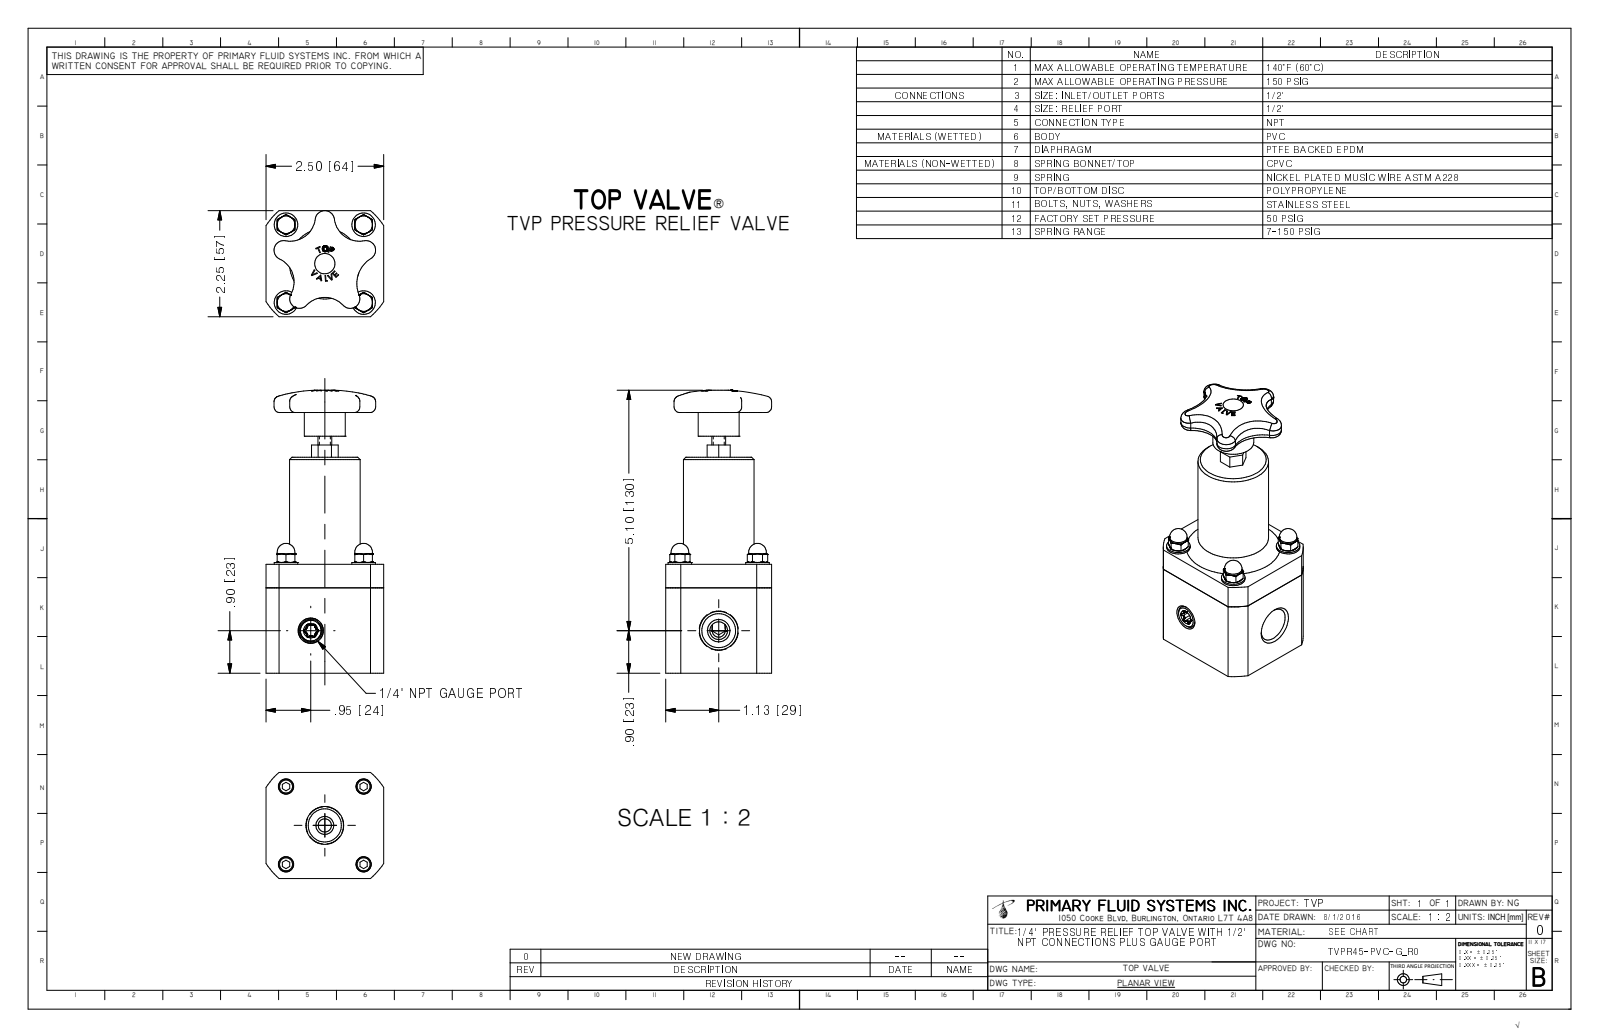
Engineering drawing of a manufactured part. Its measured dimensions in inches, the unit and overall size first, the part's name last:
Units: inches
Overall size (bounding box): 6 × 2.5 × 2.25
Round holes (diameter × count): ⌀0.147 ×4, ⌀0.703 ×1, ⌀0.719 ×1, ⌀1.525 ×1
Round bosses / shafts (diameter × count): ⌀0.5 ×4, ⌀0.375 ×4, ⌀0.312 ×4, ⌀1.5 ×1, ⌀0.87 ×1, ⌀0.293 ×1
Partial cylindrical surfaces — rounded edges, fillets, slot ends (radius × count): R0.027 ×6, R0.085 ×5, R0.205 ×5, R0.536 ×4, R0.656 ×4, R0.625 ×1, R0.745 ×1, R1.488 ×1
Main face-to-face distances: 2.25, 2.5, 2.31, 4.58, 2.27, 0.6, 1.9, 5.026, 2.716, 0.446
Hole centre spacings: 1.167, 1.167, 1.65, 1.65, 2.334
Volume: 17.33 in³ · Surface area: 60.29 in²
Bodies: 1 solid, 378 faces (155 planar, 54 cylindrical, 169 other)
Part name (STEP PRODUCT): TVPR45-PVC-G_R0
STEP written by: Autodesk Inventor 2009 (AUTOMOTIVE_DESIGN)
